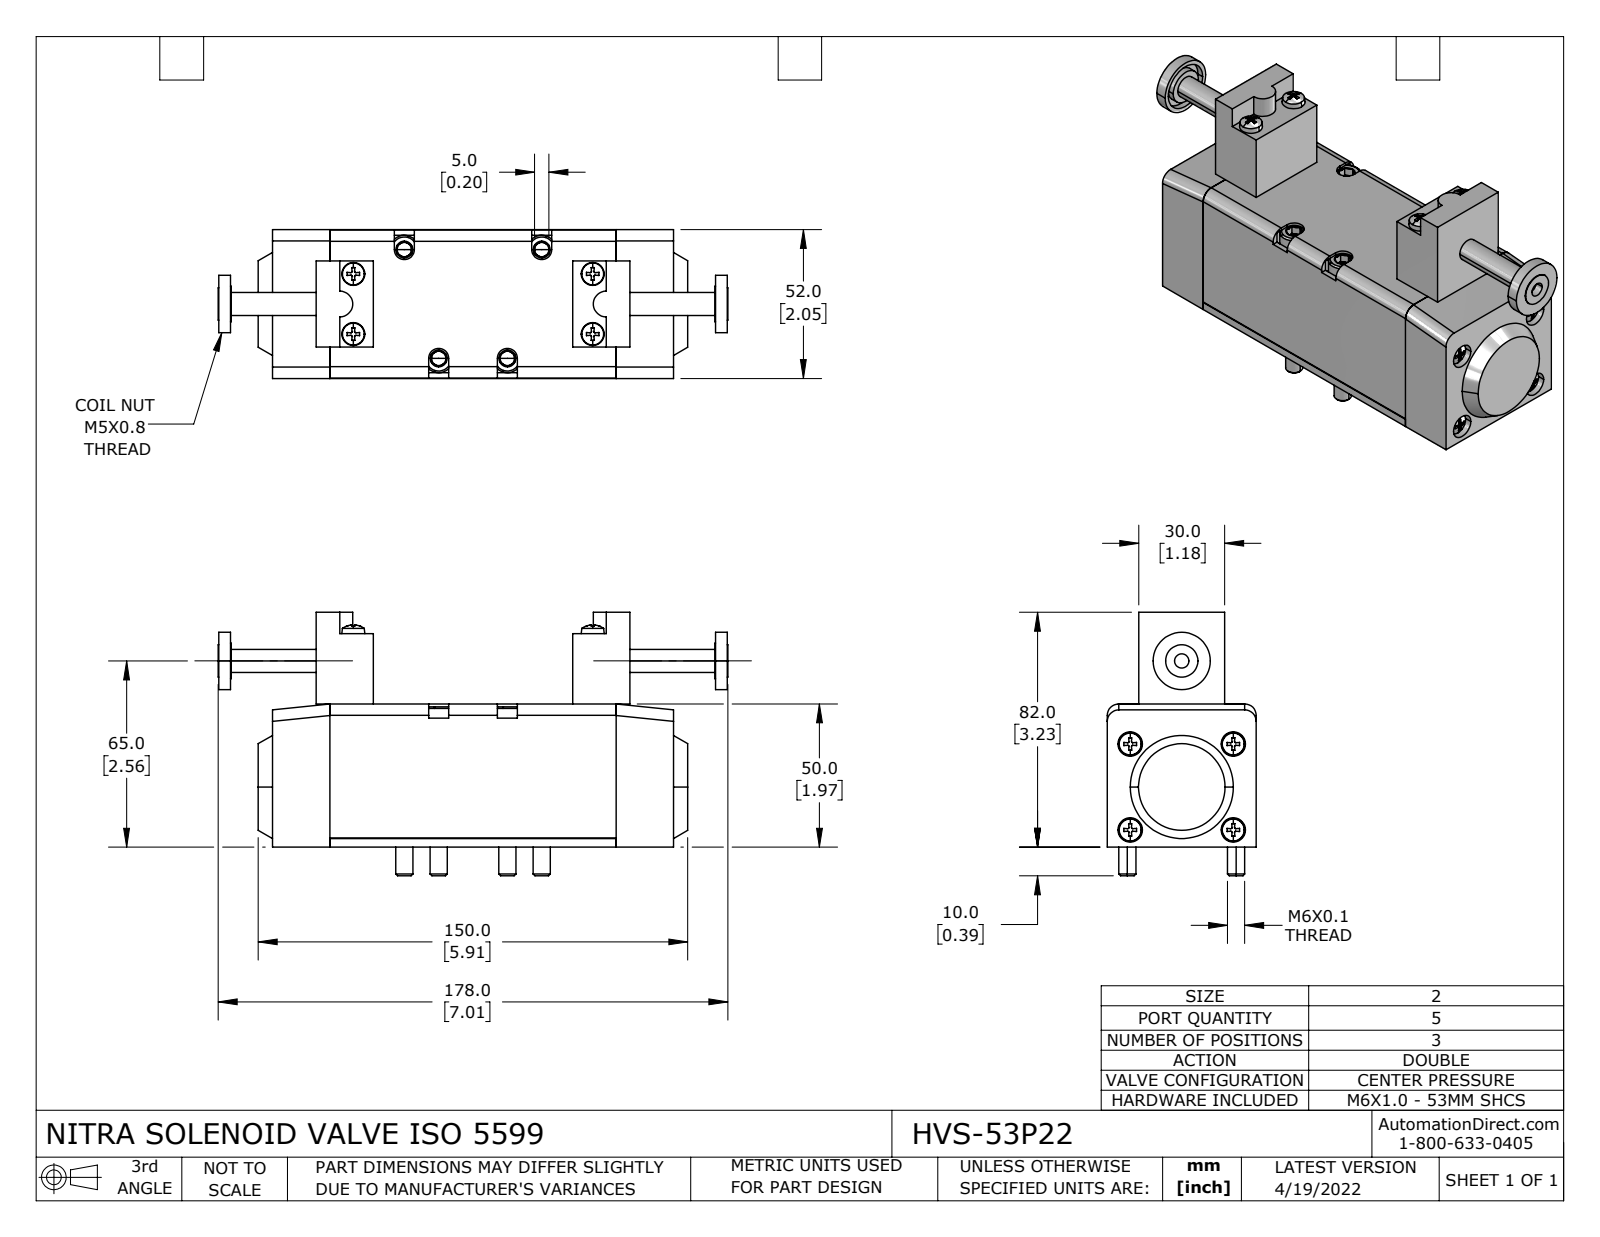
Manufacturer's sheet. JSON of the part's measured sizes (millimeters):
{"part_name": "HVS-53P22", "step_written_by": "SolidWorks 2021 (CONFIG_CONTROL_DESIGN)", "units": "millimeters", "bodies": {"solids": 21, "faces": 850, "planar": 434, "cylindrical": 156, "other": 260}, "overall_size": [178, 92, 52], "volume_mm3": 405600, "surface_area_mm2": 76970, "round_holes": [[3.3, 8], [4.1, 4], [6.5, 4], [8.5, 4], [5, 1], [16.9, 1]], "round_bosses_or_shafts": [[4, 8], [10, 4], [6, 4], [20, 1], [12.4, 1], [11.3, 1], [8, 1]], "partial_cylinders_radius": [[4, 6], [3.5, 4], [5, 4], [4.5, 2]], "face_to_face_distances": [50, 100, 51.8, 51.9, 20, 15.2, 104.8, 120, 11, 41], "hole_center_spacings": [19.7, 21, 30, 31, 34.1, 34.4, 36, 39.9]}
